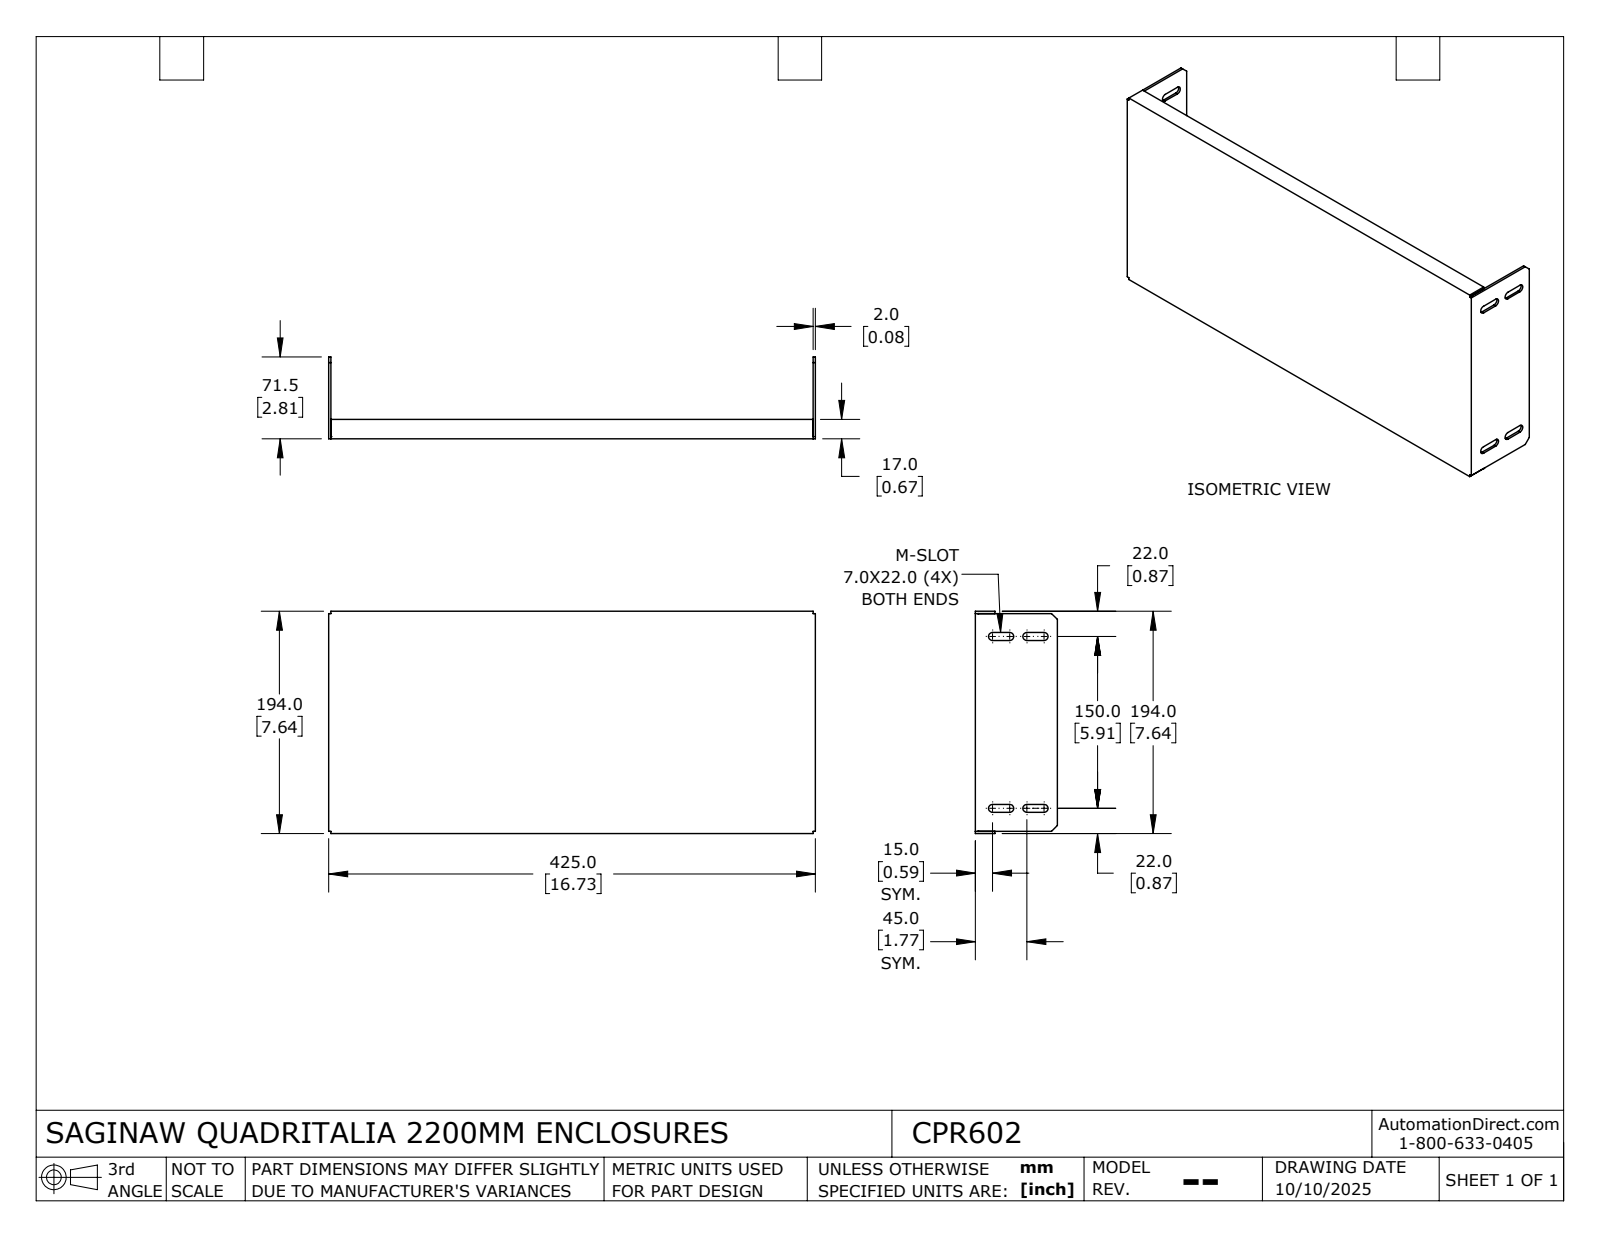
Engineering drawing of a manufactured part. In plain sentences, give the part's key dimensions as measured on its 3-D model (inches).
The part is named "CPR602_Default". Its 3-D file was written by "SolidWorks 2024 (CONFIG_CONTROL_DESIGN)". It is 1 solid with 59 faces: 43 planar, 16 cylindrical and 0 other. Overall it measures 16.732 by 7.638 by 2.815 inches. Its volume is 14.68 cubic inches and its surface area 379 square inches. Partial cylindrical surfaces (rounded edges, fillets, slot ends): 8 of radius 0.138. The main face-to-face distances are 0.079, 16.654, 7.559, 16.732, 16.575, 7.638, 7.48, 0.669, 0.591, 2.815.
